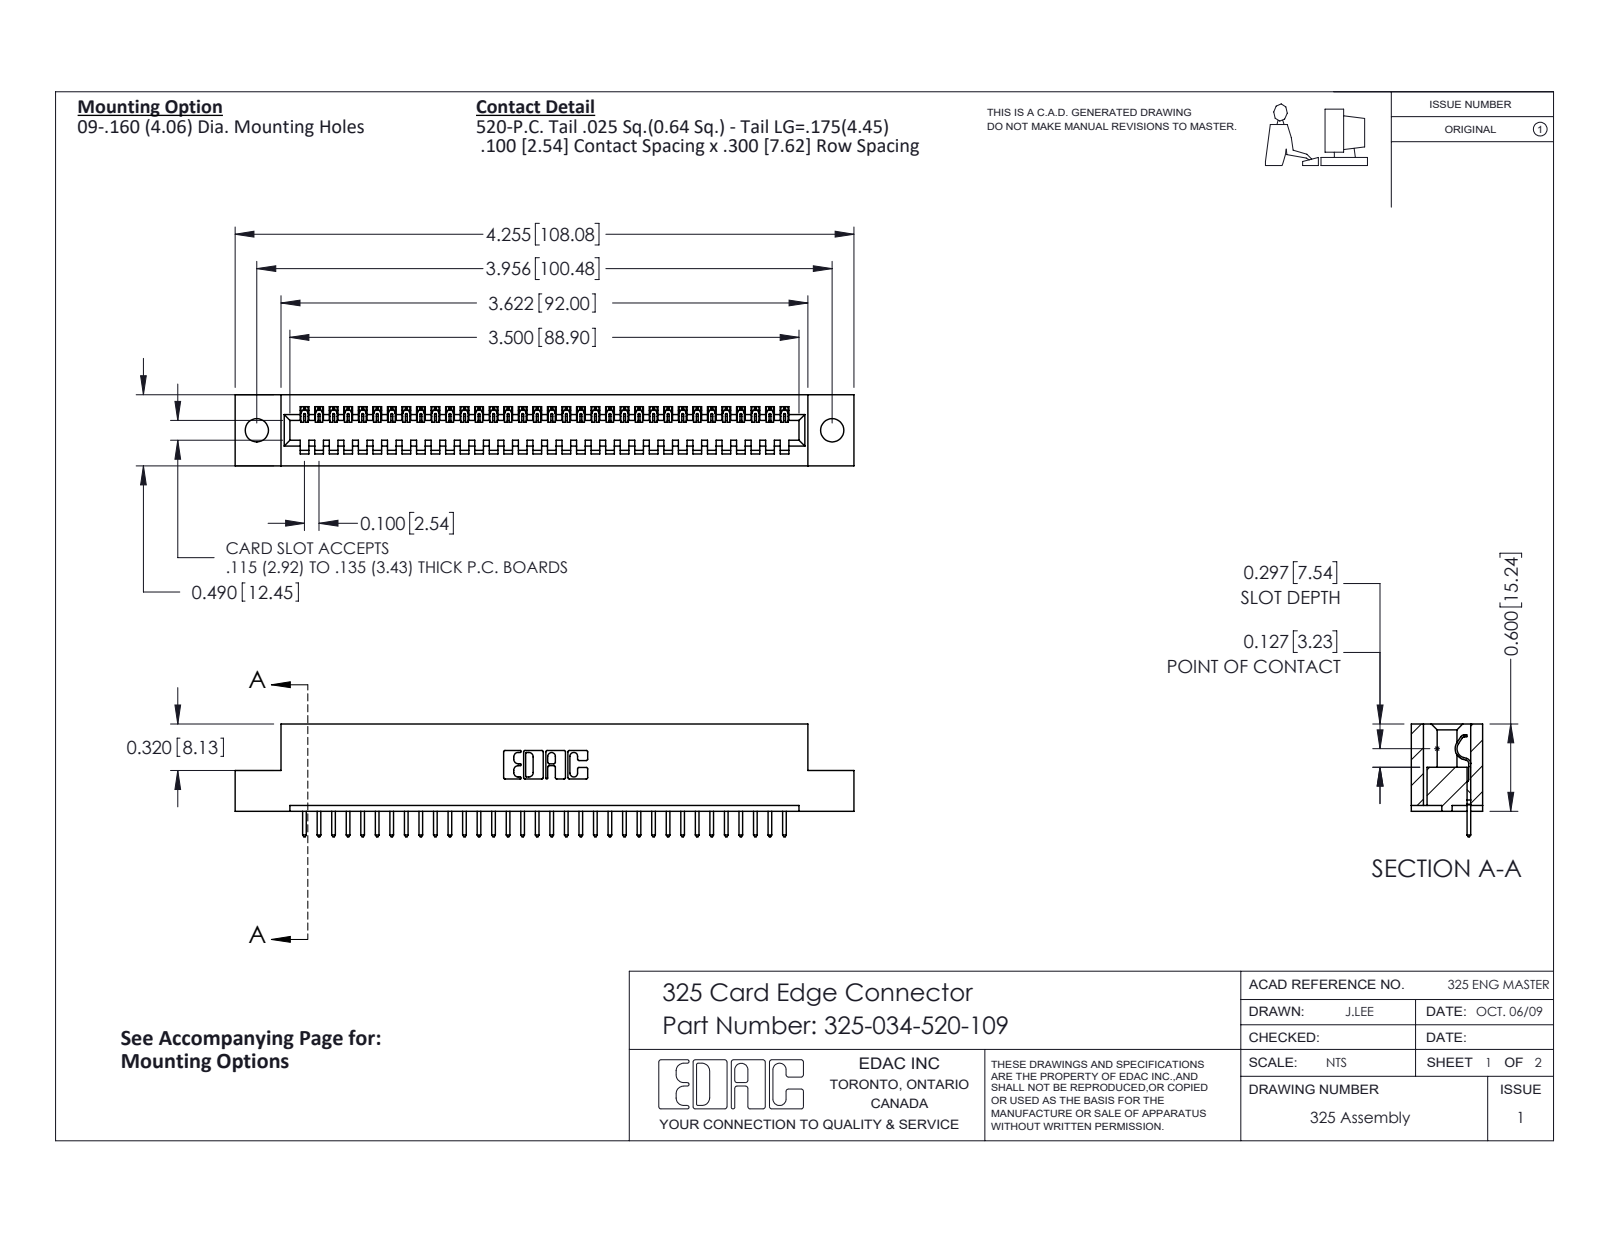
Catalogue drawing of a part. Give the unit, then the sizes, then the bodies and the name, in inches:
Units: inches
Overall size (bounding box): 4.255 × 0.775 × 0.49
Round holes (diameter × count): ⌀0.16 ×2
Partial cylindrical surfaces — rounded edges, fillets, slot ends (radius × count): R0.006 ×68, R0.01 ×68, R0.01 ×22, R0.007 ×6, R0.031 ×6, R0.026 ×3, R0.014 ×1, R0.022 ×1
Main face-to-face distances: 0.083, 0.407, 0.49, 0.3, 0.107, 0.383, 0.025, 0.325, 0.04, 0.56
Hole centre spacings: 3.956
Volume: 0.814 in³ · Surface area: 21.66 in²
Bodies: 35 solids, 2086 faces (1498 planar, 588 cylindrical, 0 other)
Part name (STEP PRODUCT): 325-292-001_325-293-120; 325 Part_.160 TH; 325-034-520-109
STEP written by: SolidWorks 2016 (CONFIG_CONTROL_DESIGN)
